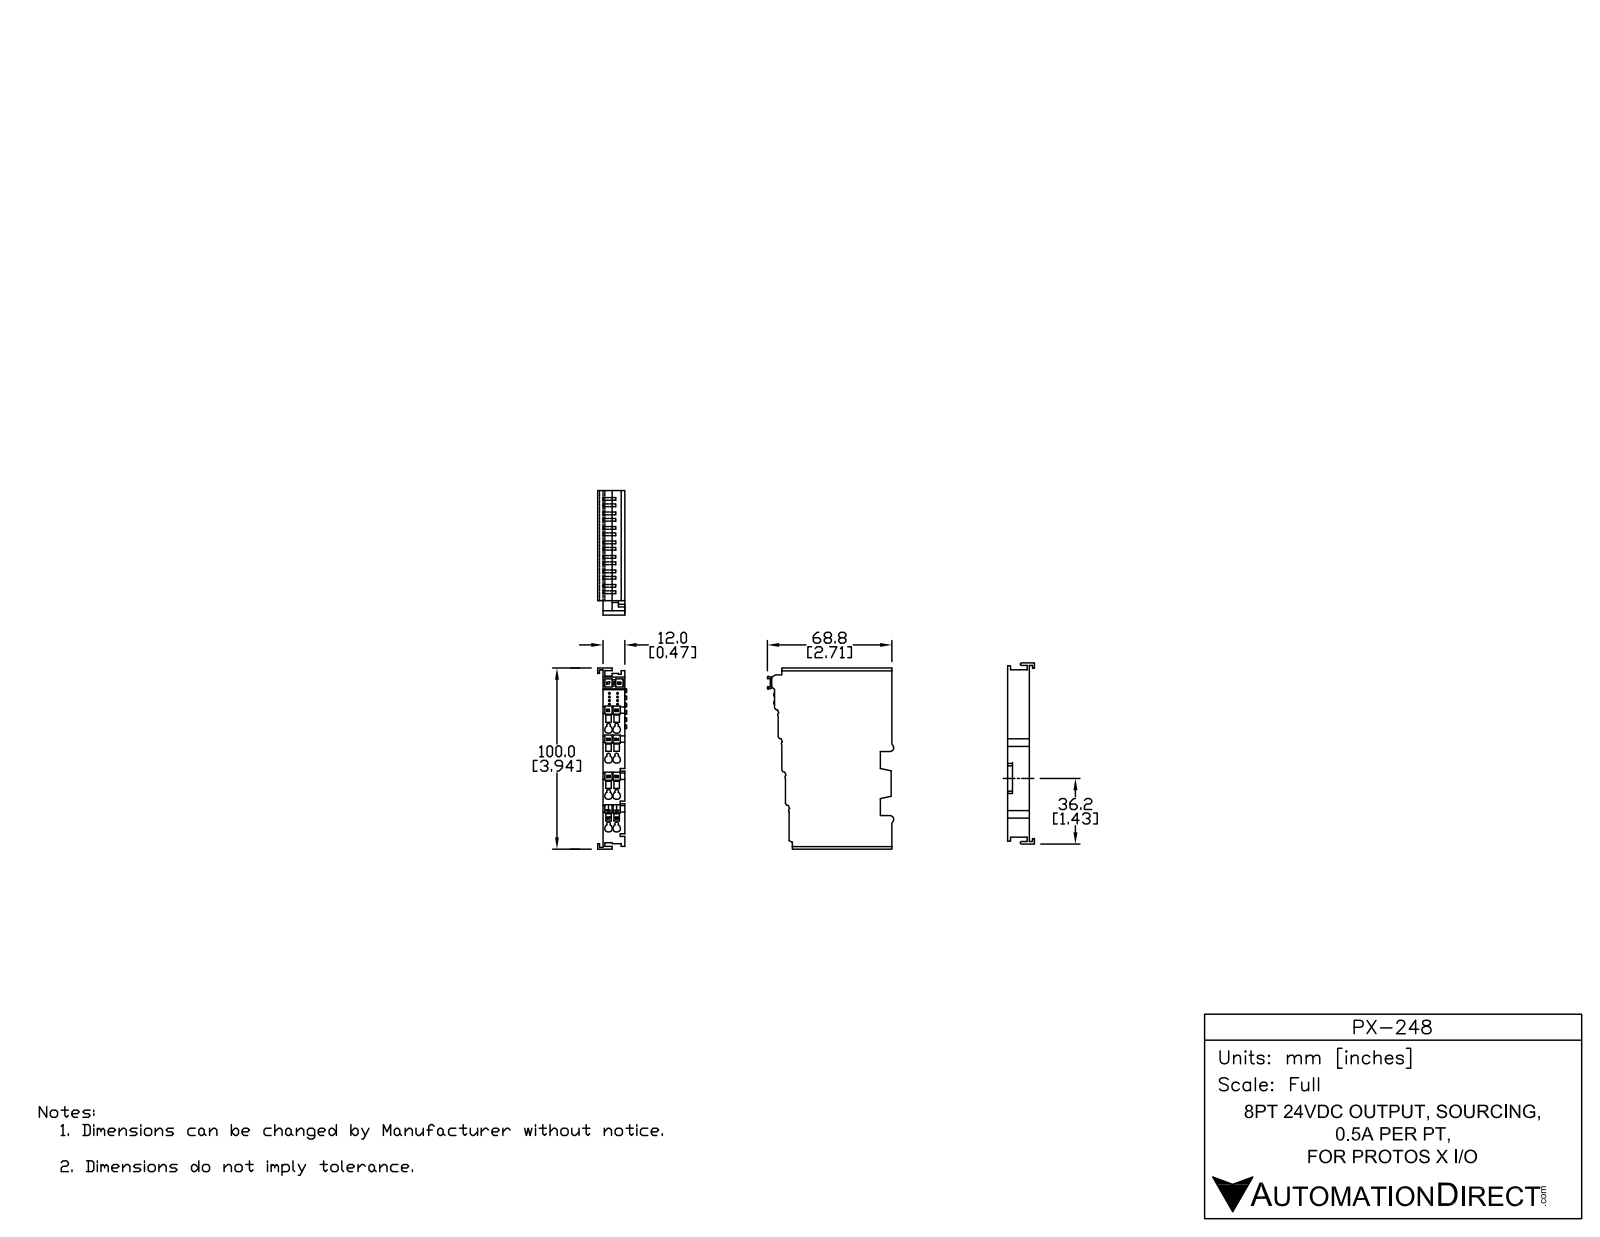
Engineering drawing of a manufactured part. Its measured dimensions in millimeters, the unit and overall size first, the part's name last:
Units: millimetres
Overall size (bounding box): 100.25 × 69.28 × 15.15
Round holes (diameter × count): ⌀4 ×8
Partial cylindrical surfaces — rounded edges, fillets, slot ends (radius × count): R0.25 ×67, R0.3 ×43, R0.38 ×12, R0.4 ×10, R1 ×8, R0.17 ×4, R1.03 ×4, R1.38 ×4
Main face-to-face distances: 12, 2, 10, 1, 1.85, 11, 4, 8.7, 3.15, 1.22
Hole centre spacings: 5, 18.4, 19.07, 16, 16.76, 34.4, 34.76, 36.8
Volume: 59 090 mm³ · Surface area: 32 341 mm²
Bodies: 26 solids, 1425 faces (1011 planar, 354 cylindrical, 60 other)
Part name (STEP PRODUCT): PX-248
STEP written by: SolidWorks 2014 (AUTOMOTIVE_DESIGN)
